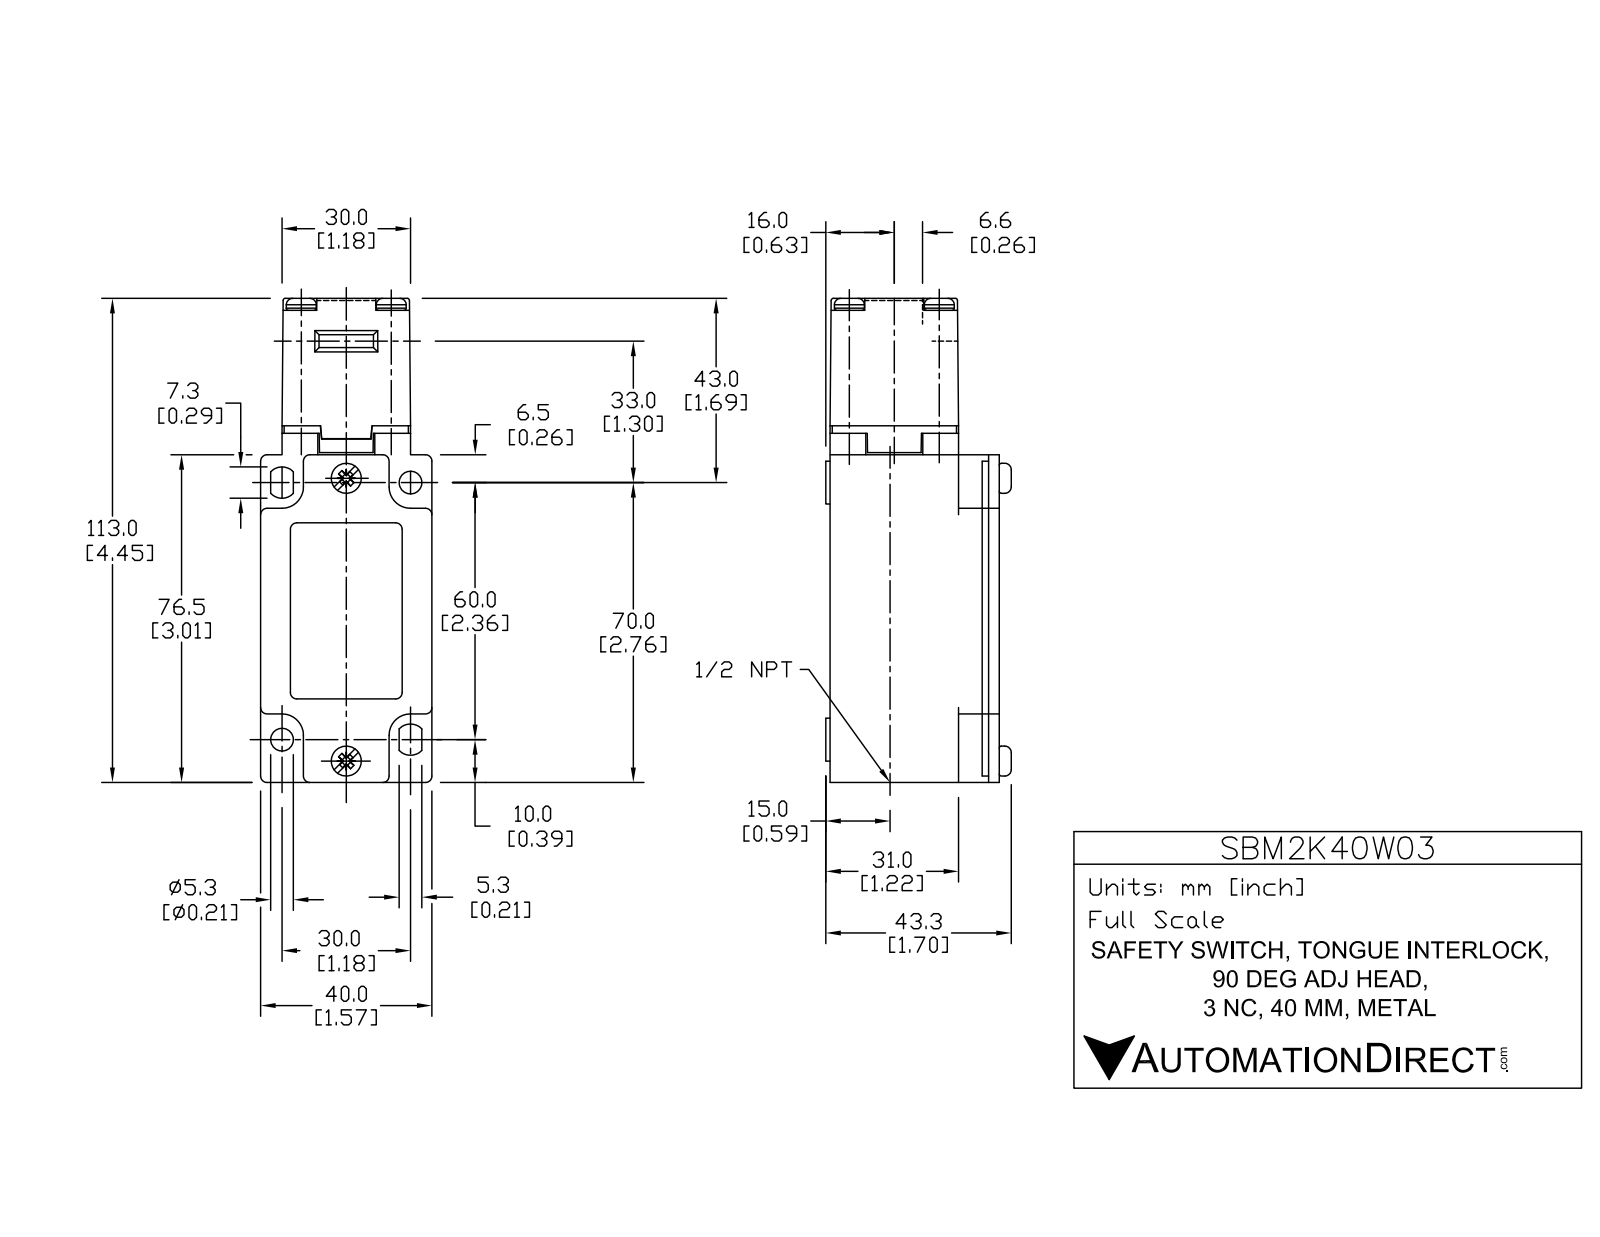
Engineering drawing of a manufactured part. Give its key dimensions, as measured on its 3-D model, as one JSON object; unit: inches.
{"part_name": "SBM2K40W03", "step_written_by": "SolidWorks 2017 (AUTOMOTIVE_DESIGN)", "units": "inches", "bodies": {"solids": 2, "faces": 183, "planar": 97, "cylindrical": 72, "other": 14}, "overall_size": [4.449, 1.705, 1.575], "volume_in3": 8.506, "surface_area_in2": 40.95, "round_holes": [[0.205, 2], [0.276, 2], [0.669, 1], [0.748, 1]], "round_bosses_or_shafts": [[0.394, 4], [0.276, 4]], "partial_cylinders_radius": [[0.059, 16], [0.02, 4], [0.197, 4], [0.128, 2], [0.453, 1], [0.472, 1]], "face_to_face_distances": [1.181, 0.197, 1.575, 1.555, 1.378, 0.374, 3.012, 0.118, 0.02, 0.984], "hole_center_spacings": [0.557, 0.827, 2.641]}
